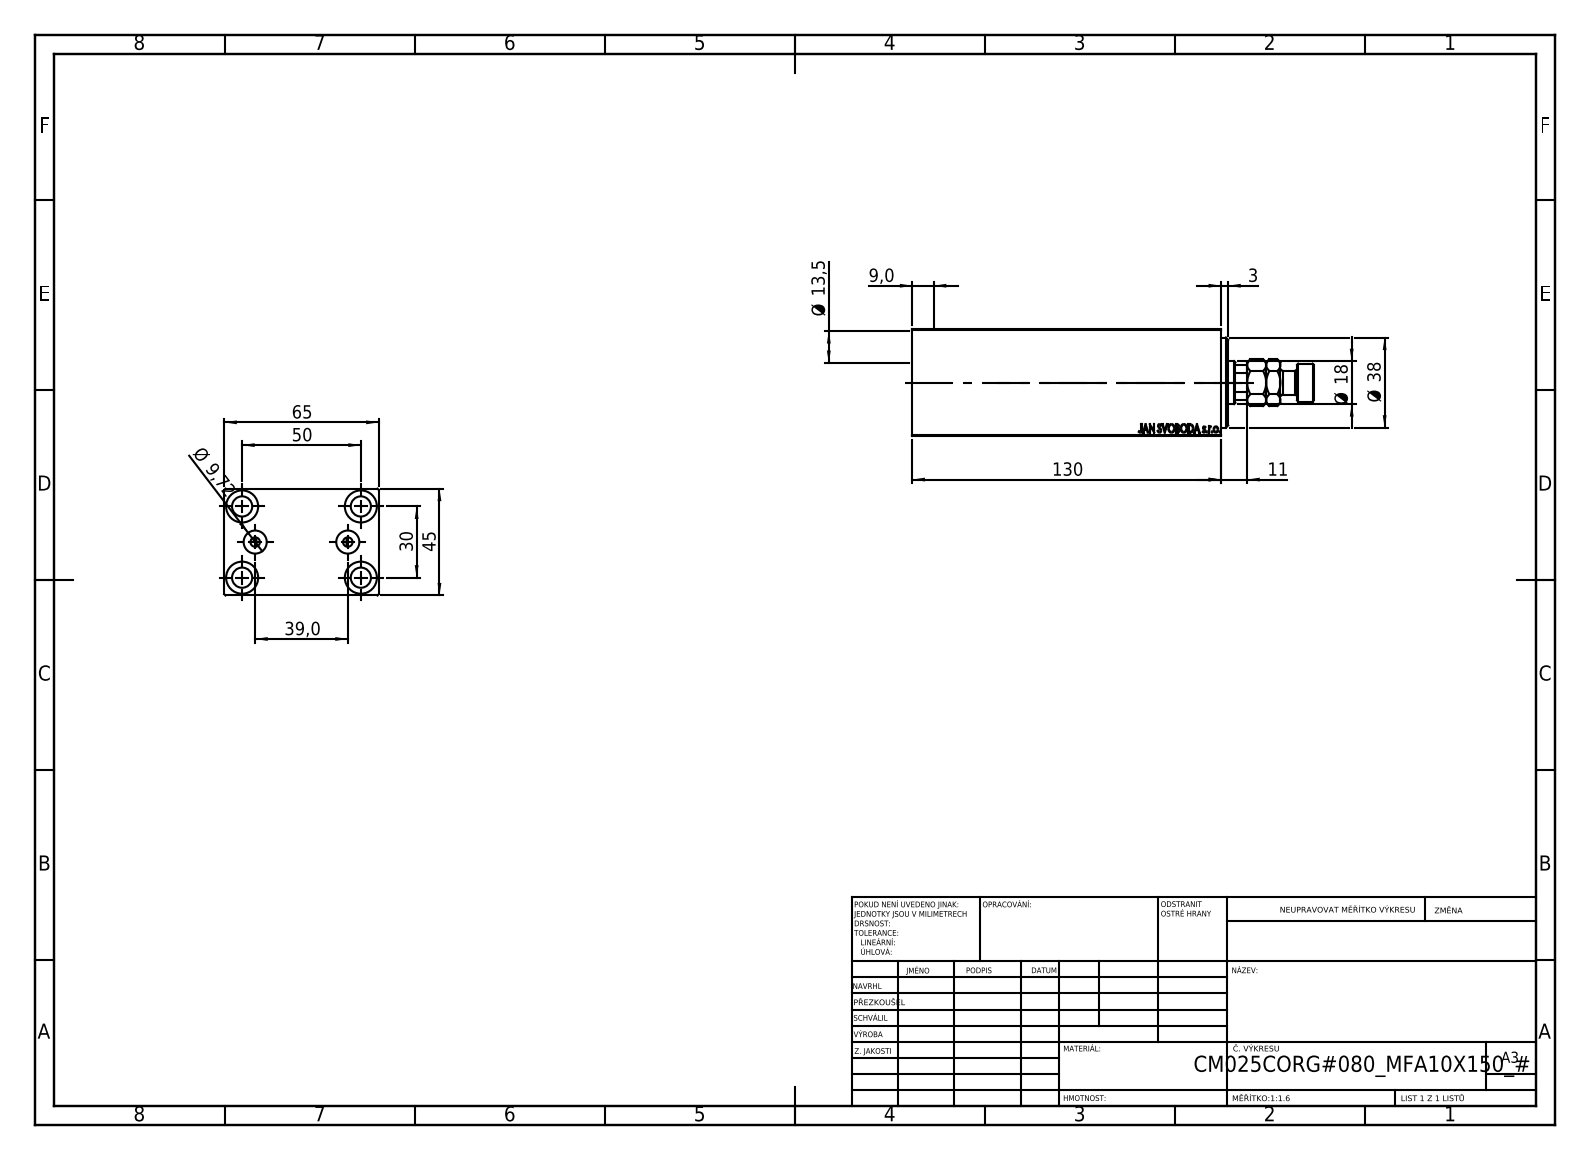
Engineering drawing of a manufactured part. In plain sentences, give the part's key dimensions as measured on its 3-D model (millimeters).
The part is named "V450CM_C_Body; MFA; V450CM_C_VCP; V450CM_VC_B". Its 3-D file was written by "SolidWorks 2019 (CONFIG_CONTROL_DESIGN)". It is 4 solids with 910 faces: 424 planar, 60 cylindrical and 426 other. Overall it measures 169 by 65 by 45 millimeters. Its volume is 330 576 cubic millimeters and its surface area 78 136 square millimeters. Round holes: 5 of diameter 8.5, 4 of diameter 13.5, 2 of diameter 4, 2 of diameter 9.72, 1 of diameter 18, 1 of diameter 21.5, 1 of diameter 25, 1 of diameter 27, 1 of diameter 38. Round bosses or shafts: 1 of diameter 16, 1 of diameter 10. Partial cylindrical surfaces (rounded edges, fillets, slot ends): 1 of radius 8.5. The main face-to-face distances are 45, 65, 6, 119, 124, 130, 125, 5, 3, 8. The hole center spacings are 15.98, 29.15, 46.96, 19.5, 30, 50, 58.31, 39.
